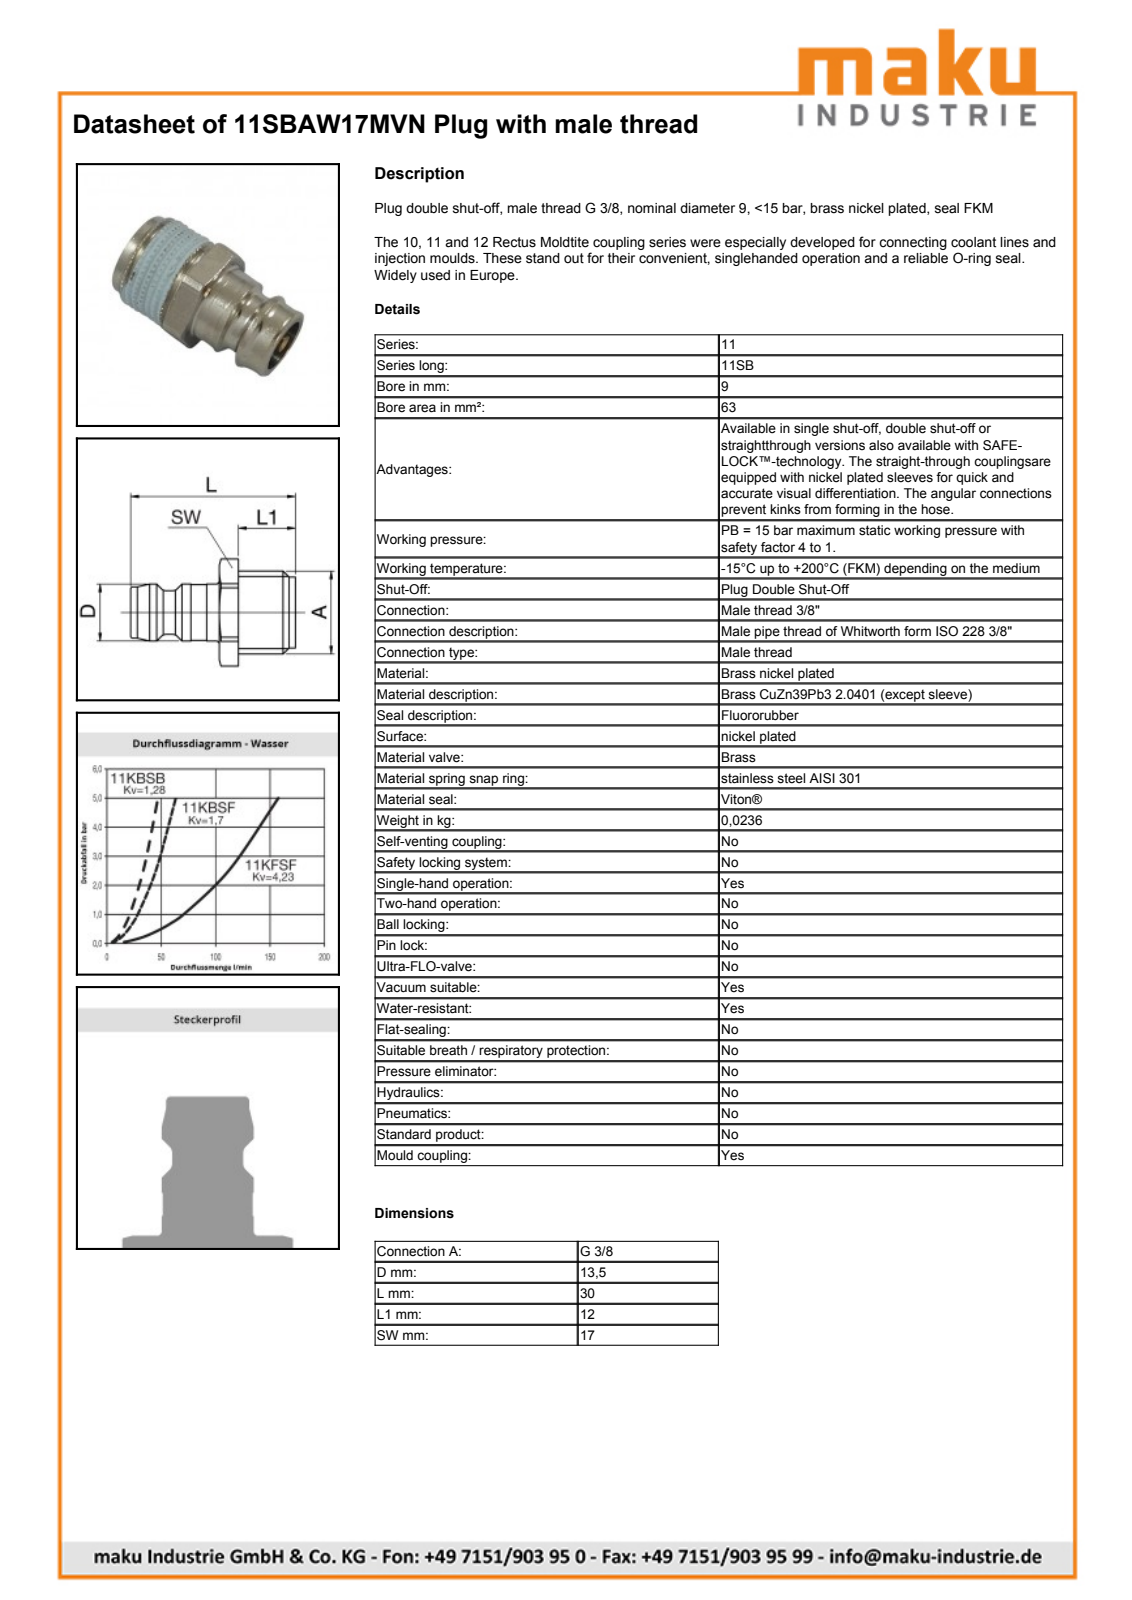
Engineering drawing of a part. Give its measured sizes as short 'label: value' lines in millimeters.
name: D107179
written by: Autodesk Inventor 2013 (AUTOMOTIVE_DESIGN)
unit: mm
bodies: 1 solid, 41 faces (12 planar, 14 cylindrical, 15 other)
size: 30 × 19.15 × 17
volume: 5 274 mm³; area: 1 885 mm²
bosses: 1× ⌀16.66, 1× ⌀14.6, 1× ⌀13.5, 1× ⌀13.3, 1× ⌀12.5, 1× ⌀10.8
rounds: 1× R9.57
face distances: 17, 30, 14, 16, 4, 18, 12, 10, 8, 20
